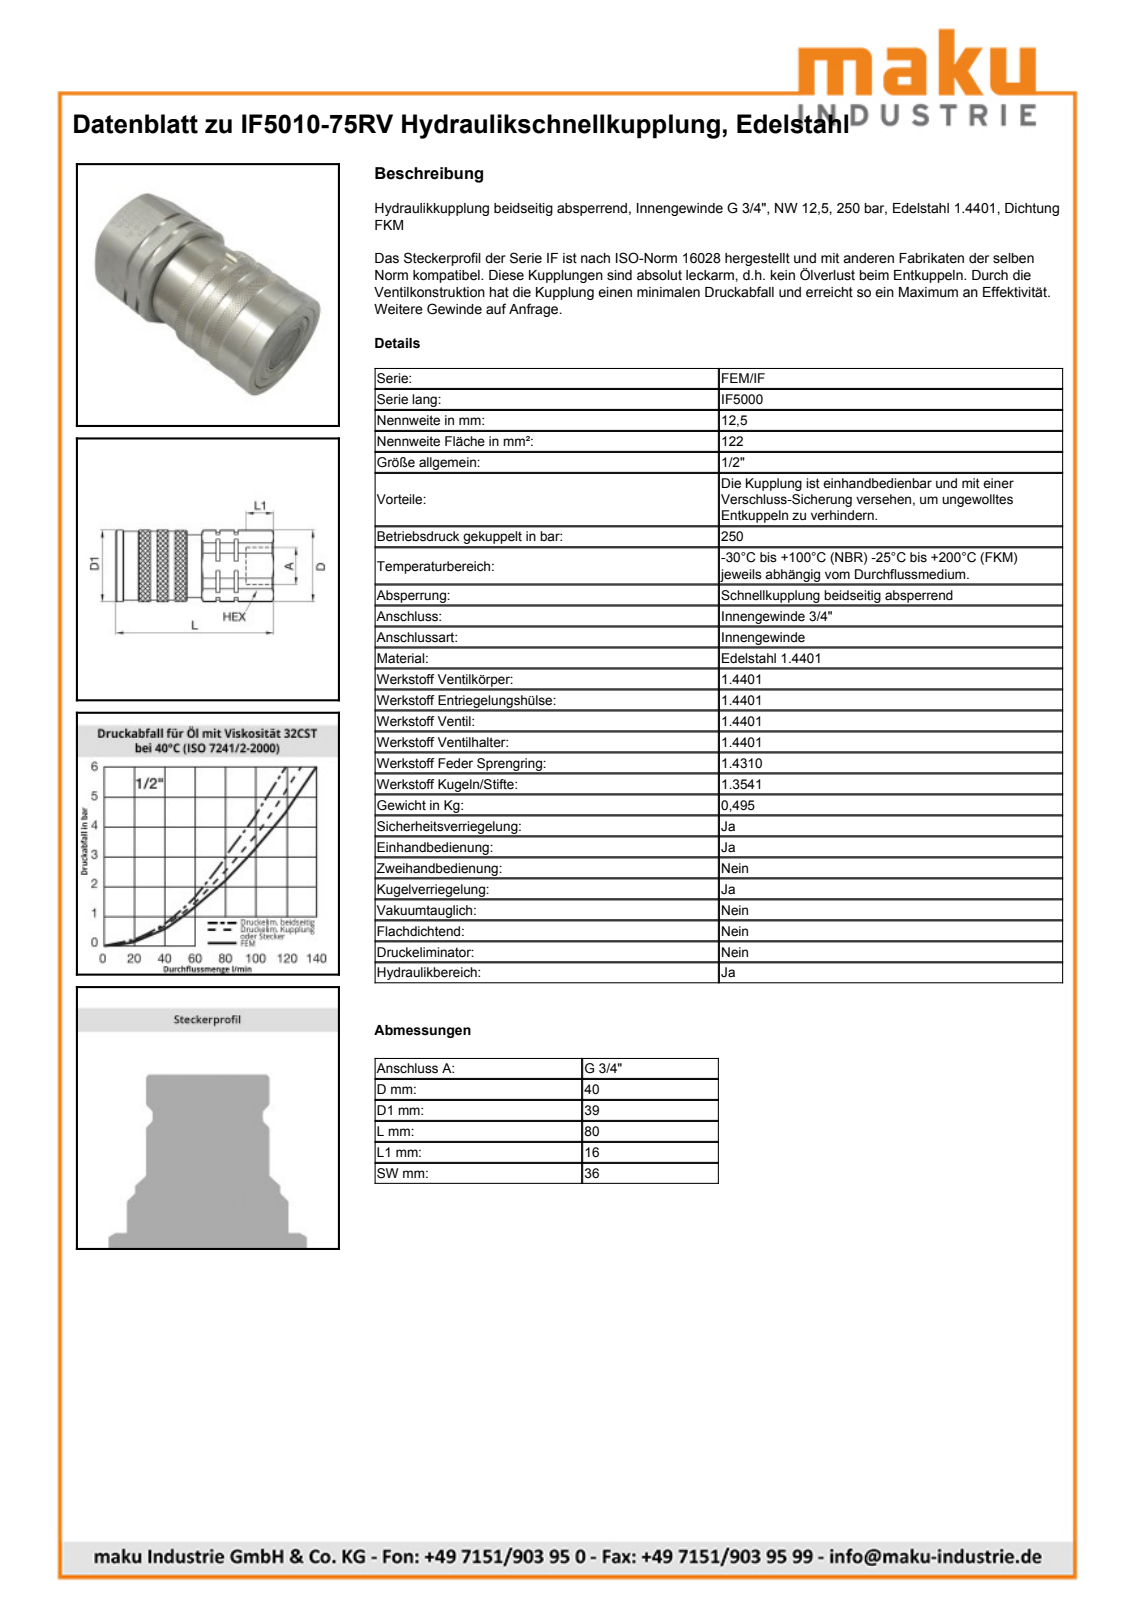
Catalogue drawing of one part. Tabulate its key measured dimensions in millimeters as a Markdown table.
| quantity | value |
| --- | --- |
| part name | IF5010-75RV |
| STEP written by | SolidWorks 2009 (AUTOMOTIVE_DESIGN) |
| units | millimeters |
| bodies | 1 solid, 171 faces (62 planar, 63 cylindrical, 46 other) |
| overall size | 80 × 40 × 38 |
| volume | 76 659 mm³ |
| surface area | 15 731 mm² |
| round holes (diameter × count) | 2 × 1, 15.75 × 1, 24.12 × 1, 24.7 × 1, 30.7 × 1, 34.4 × 1 |
| round bosses / shafts (diameter × count) | 38 × 1, 36.7 × 1, 36 × 1, 34 × 1, 32.32 × 1, 30 × 1, 24.5 × 1, 15.51 × 1 |
| partial cylindrical surfaces (radius × count) | 0.5 × 2, 20 × 1 |
| main face-to-face distances | 36, 80, 79.6, 0.4, 43.6, 44, 1.85, 8.35, 18.3, 7.8 |
